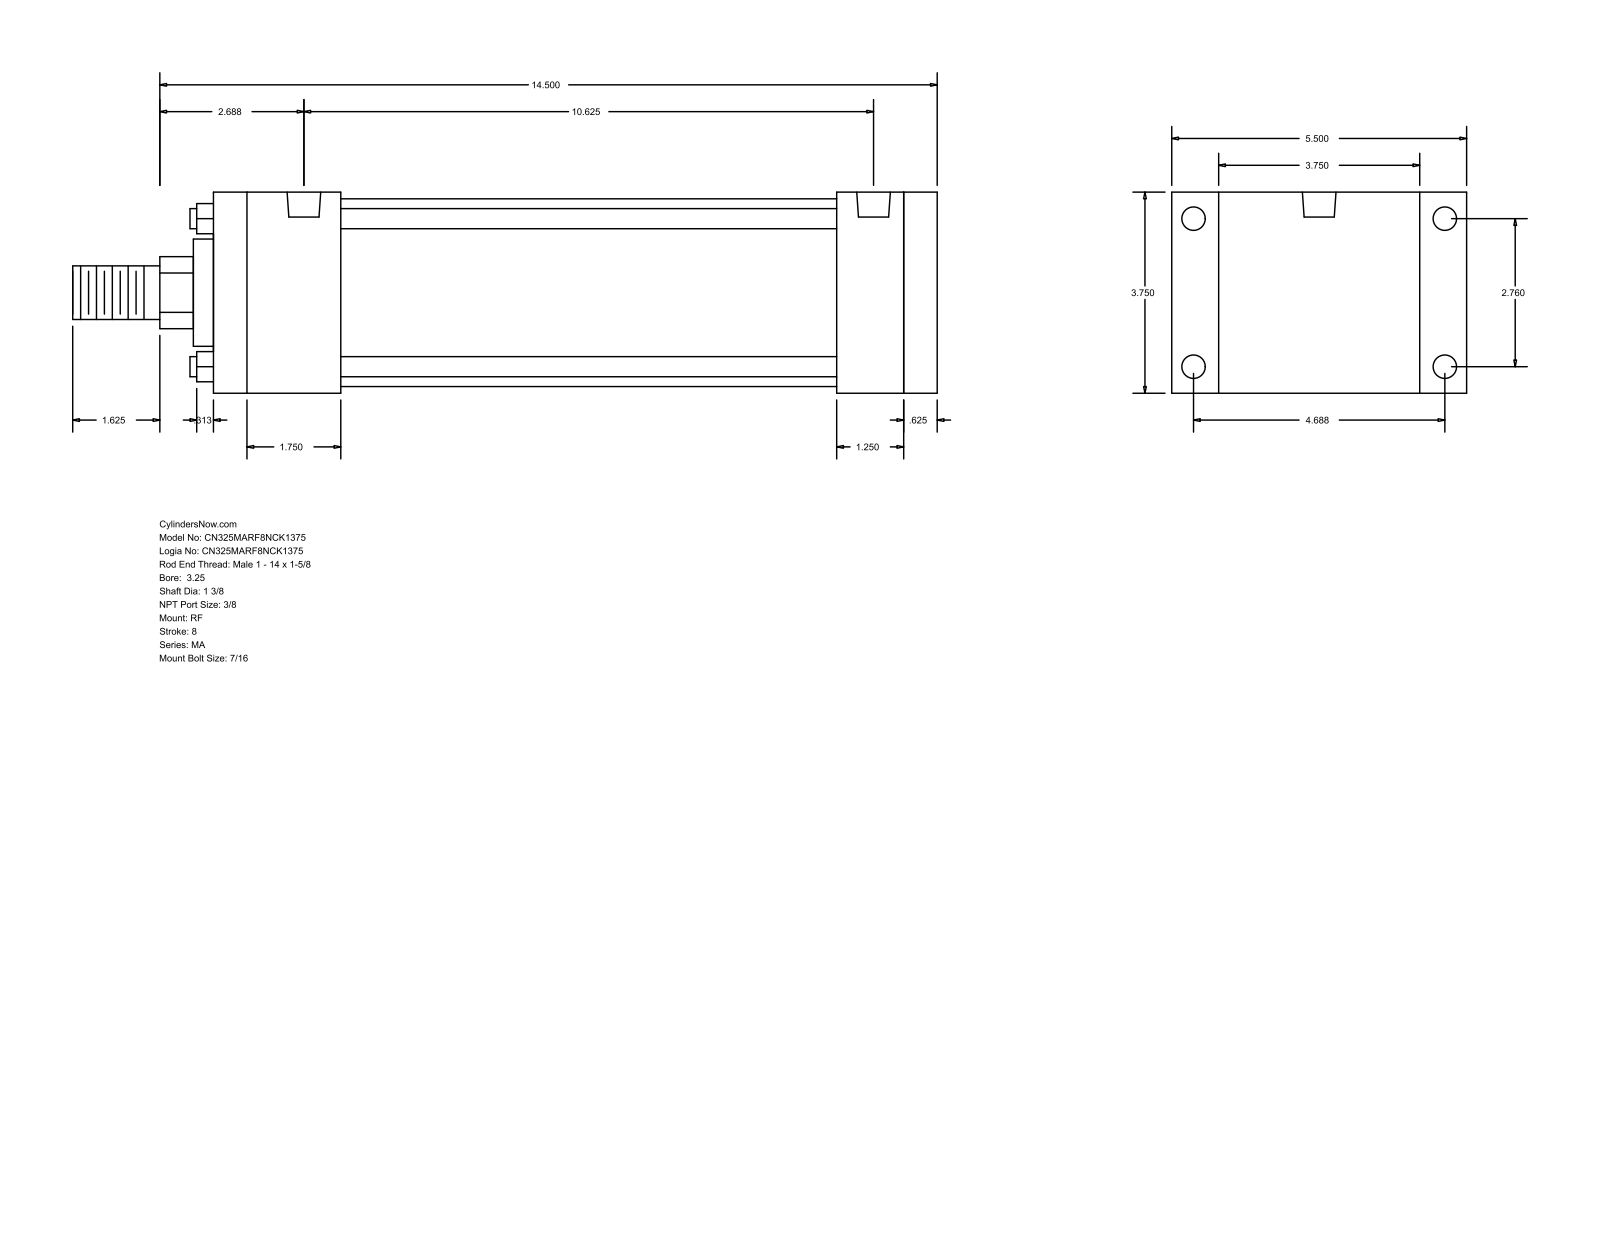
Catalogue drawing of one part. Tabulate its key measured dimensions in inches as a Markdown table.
| quantity | value |
| --- | --- |
| part name | MA_RF__0325_1.375 |
| STEP written by | GSSL Pune (CONFIG_CONTROL_DESIGN) |
| units | inches |
| bodies | 0 solids, 92 faces (64 planar, 28 cylindrical, 0 other) |
| overall size | 16.125 × 5.5 × 3.75 |
| round holes (diameter × count) | 0.437 × 8, 0.627 × 2 |
| round bosses / shafts (diameter × count) | 0.375 × 4, 3.5 × 1, 2 × 1, 1.375 × 1, 1 × 1 |
| partial cylindrical surfaces (radius × count) | 0.672 × 1 |
| main face-to-face distances | 3.75, 13.5, 12.875, 0.625, 0.875, 4.625, 11.625, 1.25, 1.875, 2.375 |
| hole center spacings | 2.76, 4.687, 5.439, 10.25, 0.187, 0.188, 10.437, 10.438 |
